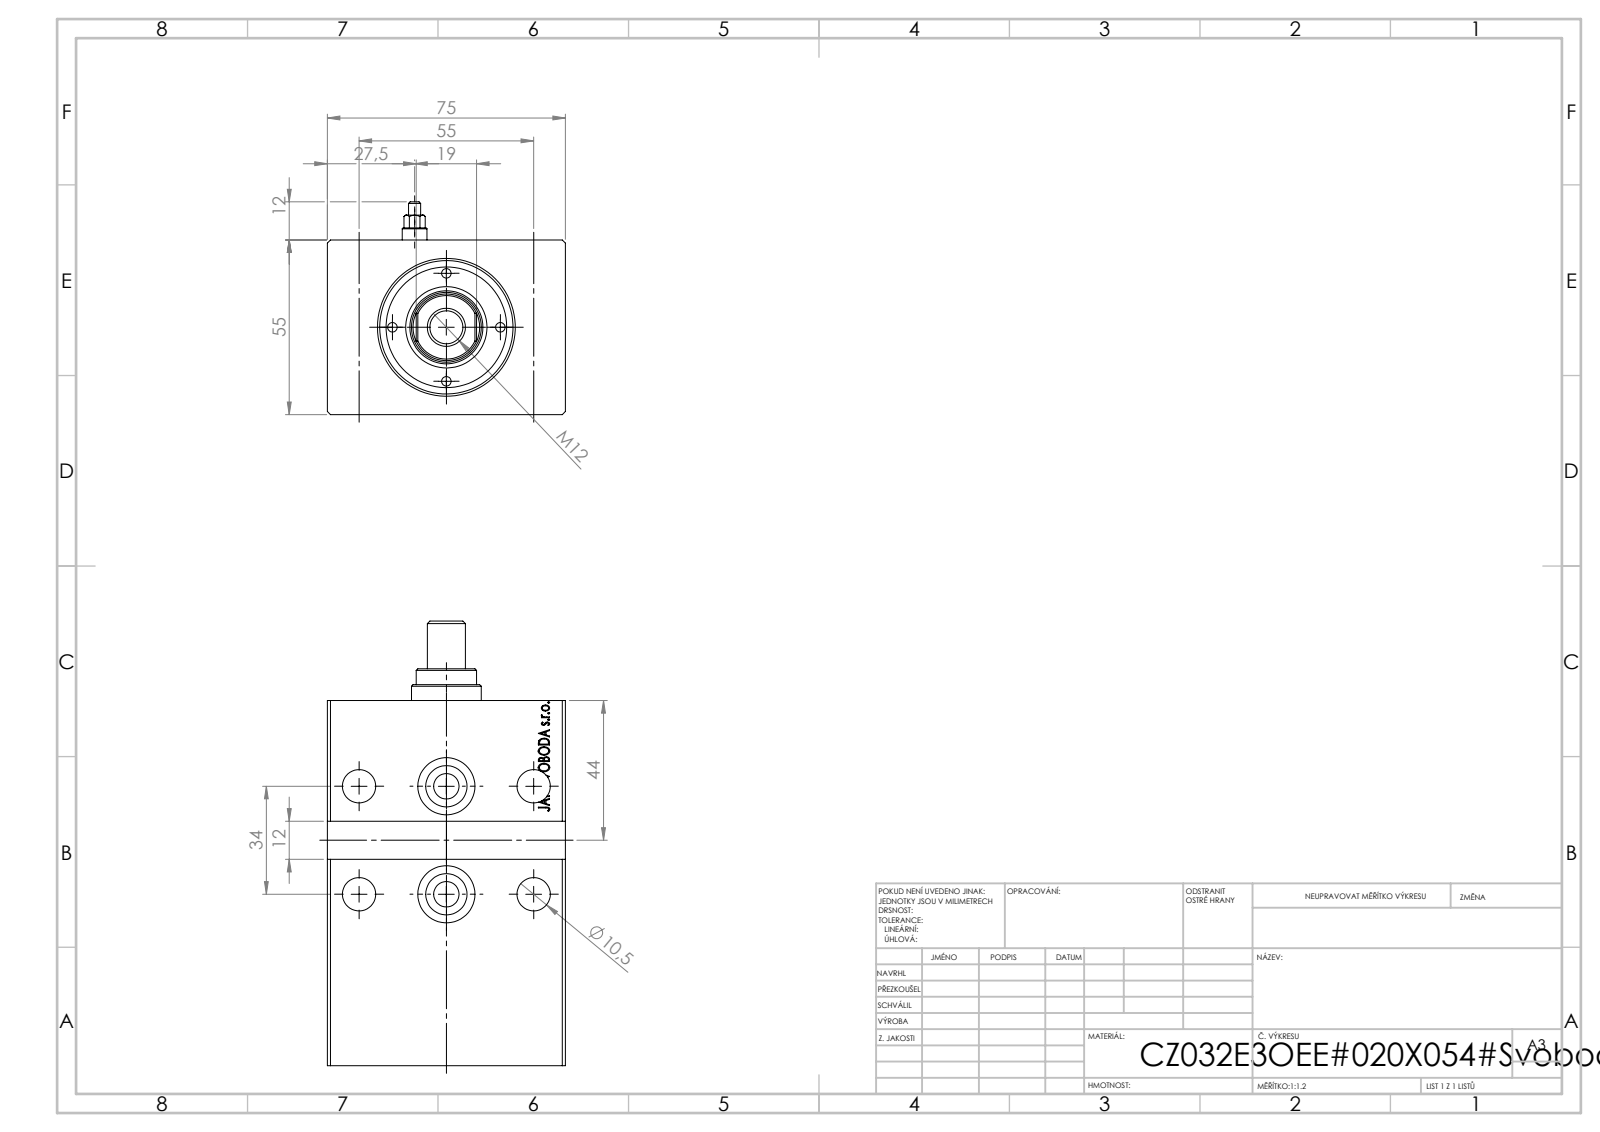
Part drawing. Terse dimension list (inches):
name: V500CZ_VCP_E; V500CZ_SMALL_MALE_METRIC; V500CZ_B_VC; Zatka_Cushioning3 (+1 more)
written by: SolidWorks 2019 (CONFIG_CONTROL_DESIGN)
unit: in
bodies: 6 solids, 862 faces (402 planar, 68 cylindrical, 392 other)
size: 5.512 × 2.953 × 2.638
volume: 27.24 in³; area: 114.4 in²
holes: 5× ⌀0.413, 4× ⌀0.118, 4× ⌀0.315, 2× ⌀0.071, 2× ⌀0.709, 1× ⌀0.866, 1× ⌀0.906, 1× ⌀1.26, 1× ⌀1.417, 1× ⌀1.654
bosses: 2× ⌀0.512, 2× ⌀0.307, 2× ⌀0.15, 1× ⌀1.496, 1× ⌀0.472
rounds: 1× R0.413
face distances: 2.165, 2.953, 4.528, 0.394, 3.984, 0.543, 3.591, 4.134, 4.52, 4.126
hole spacings: 1.339, 0.669, 0.946, 1.083, 1.722, 2.165, 2.546, 0.459
